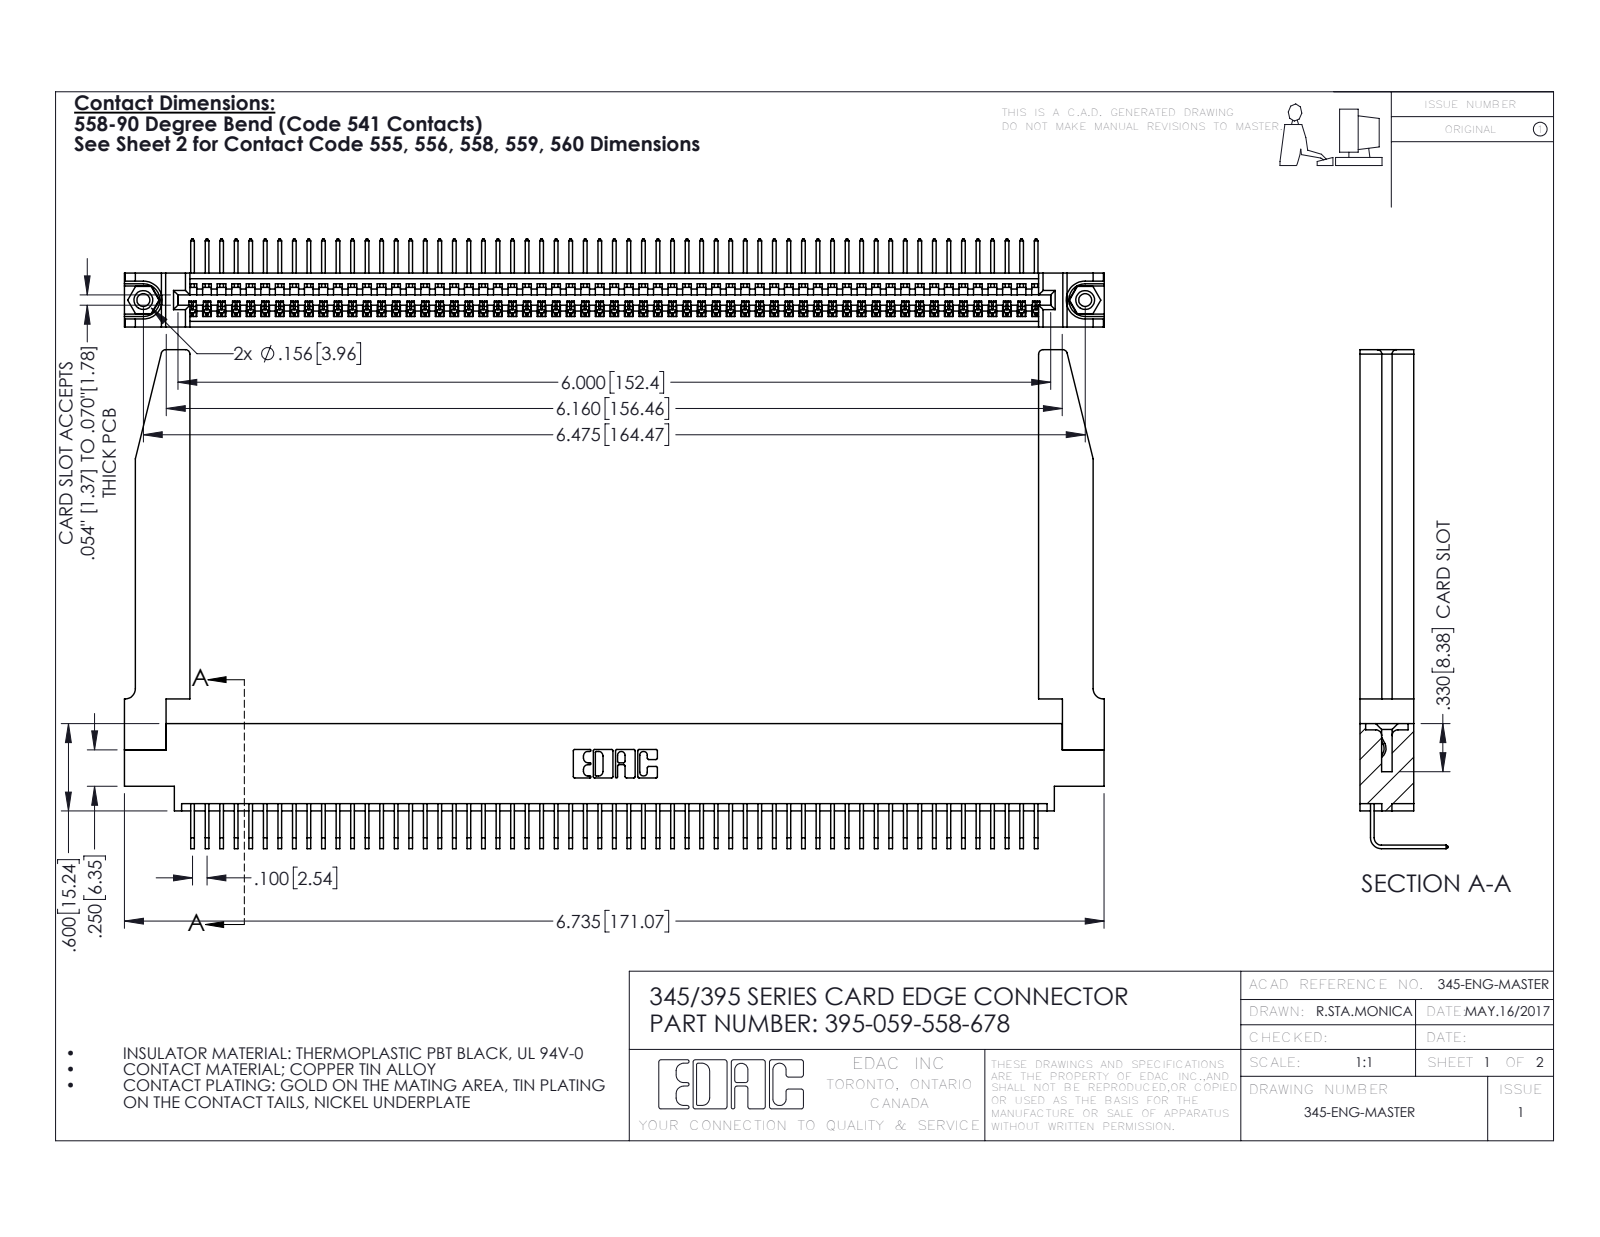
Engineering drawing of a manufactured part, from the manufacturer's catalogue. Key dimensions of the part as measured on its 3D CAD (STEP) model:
Part name (STEP PRODUCT): 345 Part_0.170 Offset - 0.156 Dia-TH; 345-250-001_345-250-001-102; 345-292-001_558 Tail - 2; 395-059-558-678 (+1 more)
STEP written by: SolidWorks 2016 (CONFIG_CONTROL_DESIGN)
Units: inches
Bodies: 64 solids, 3904 faces (2704 planar, 1148 cylindrical, 52 other)
Overall size (bounding box): 6.736 × 3.429 × 0.605
Volume: 1.479 in³ · Surface area: 46.89 in²
Round holes (diameter × count): ⌀0.089 ×2, ⌀0.125 ×2, ⌀0.156 ×2, ⌀0.064 ×1
Round bosses / shafts (diameter × count): ⌀0.155 ×2
Partial cylindrical surfaces — rounded edges, fillets, slot ends (radius × count): R0.006 ×118, R0.01 ×22, R0.03 ×8, R0.007 ×6, R0.031 ×6, R0.026 ×3, R0.031 ×2, R0.04 ×2
Main face-to-face distances: 0.37, 0.072, 0.298, 0.098, 0.272, 0.025, 0.2, 0.225, 0.148, 0.15
Hole centre spacings: 0.27, 6.239, 6.475
